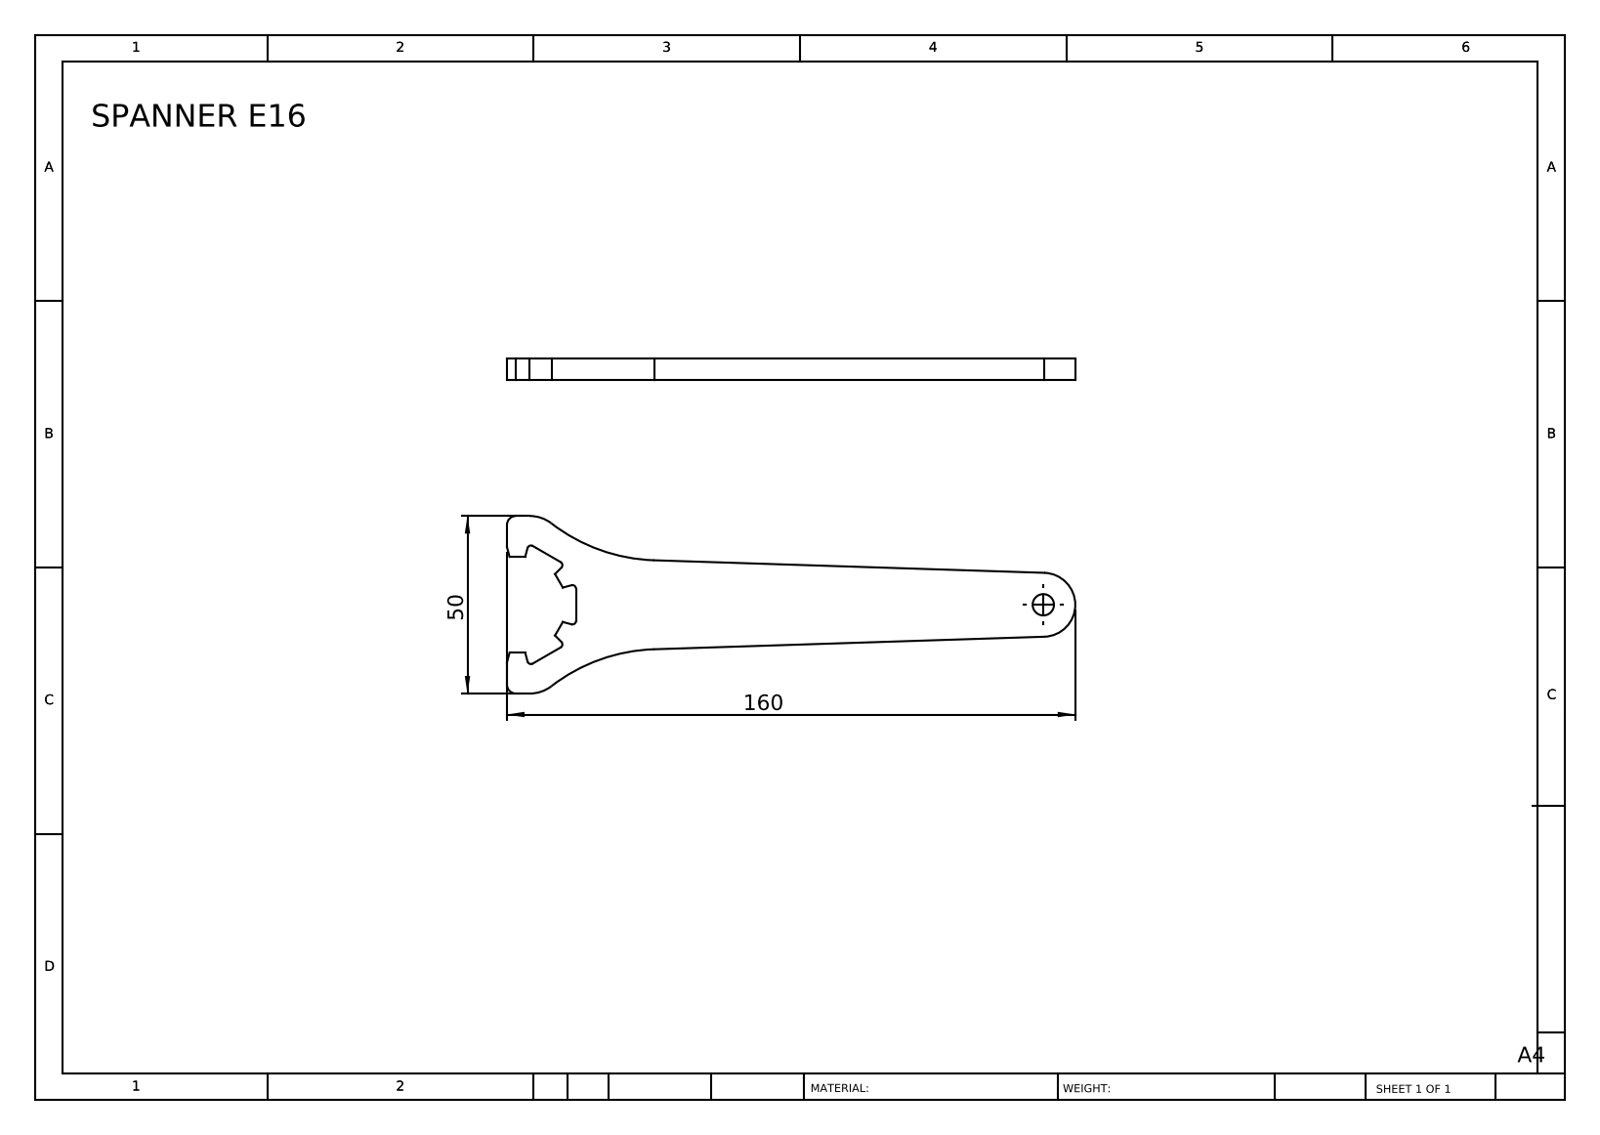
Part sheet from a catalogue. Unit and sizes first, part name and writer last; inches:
Units: inches
Overall size (bounding box): 6.299 × 1.969 × 0.236
Round holes (diameter × count): ⌀0.236 ×1
Partial cylindrical surfaces — rounded edges, fillets, slot ends (radius × count): R0.039 ×6, R0.098 ×2, R0.394 ×2, R1.969 ×2, R0.354 ×1
Main face-to-face distances: 0.236, 0.765, 0.453, 1.516, 0.108, 1.063, 1.969
Volume: 1.291 in³ · Surface area: 15.09 in²
Bodies: 1 solid, 38 faces (23 planar, 15 cylindrical, 0 other)
Part name (STEP PRODUCT): SPANNER E16
STEP written by: SolidWorks 2014 (CONFIG_CONTROL_DESIGN)
